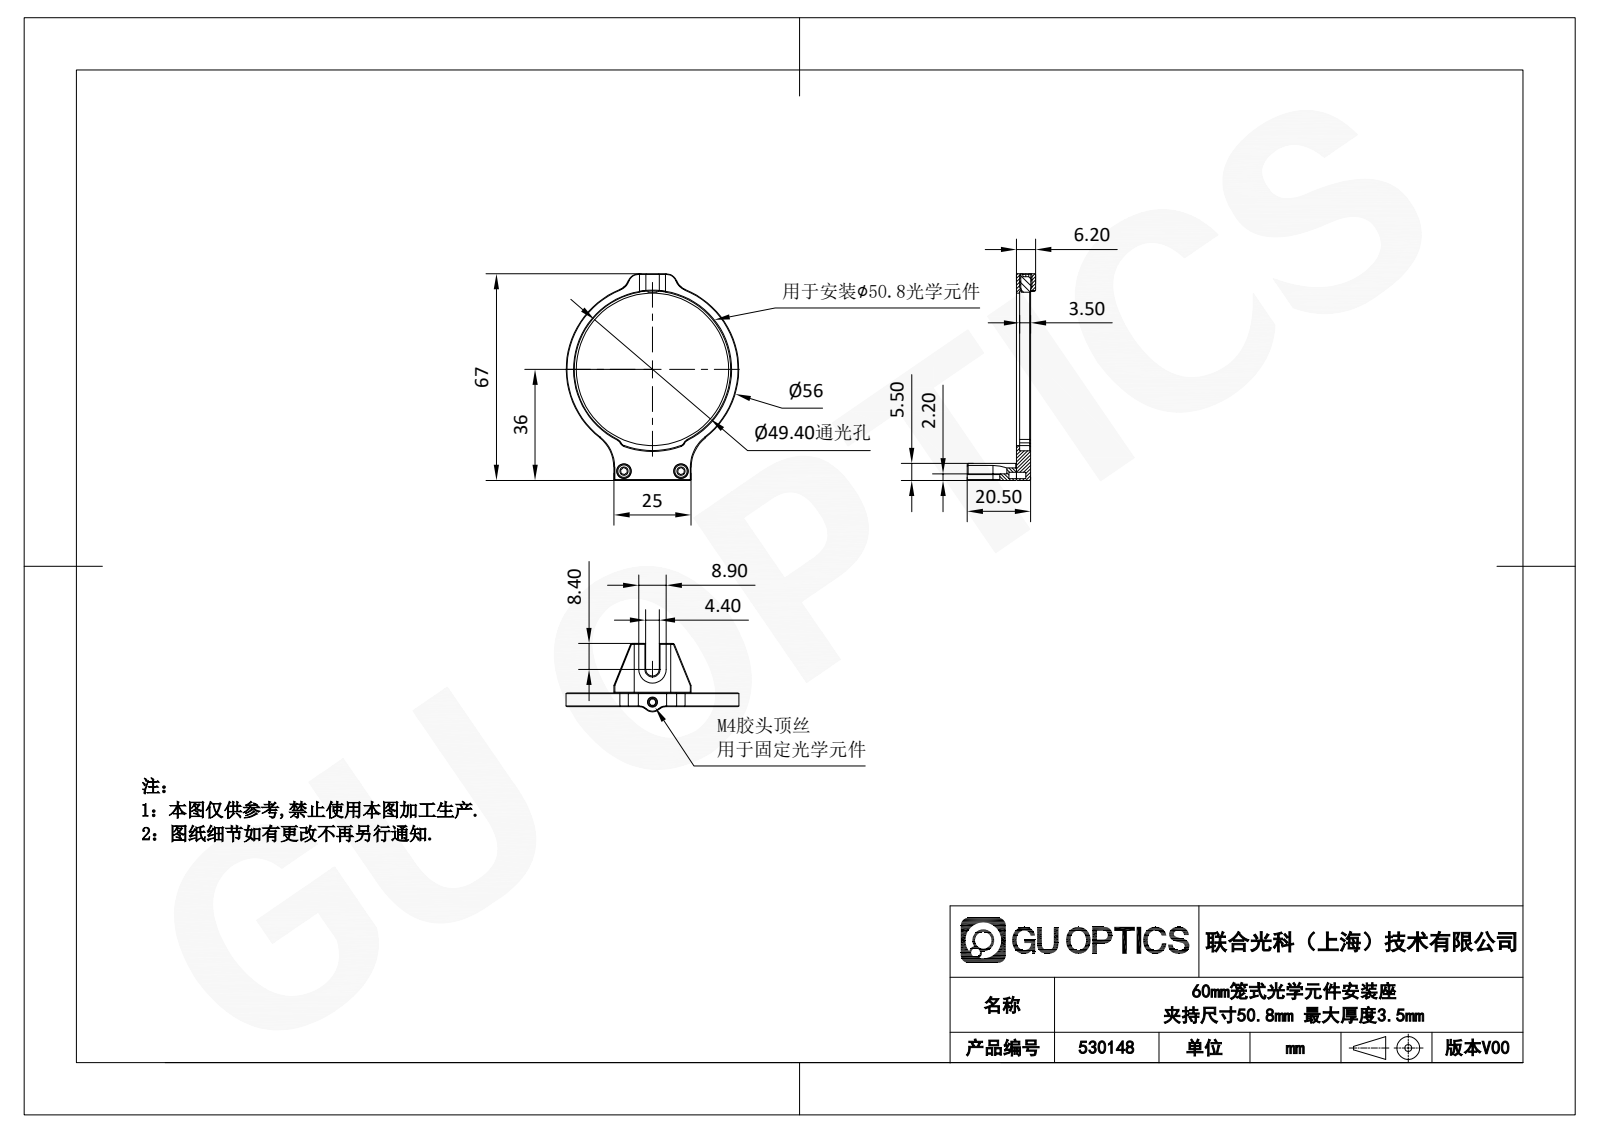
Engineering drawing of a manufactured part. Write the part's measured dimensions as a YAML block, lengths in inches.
part_name: "530148"
step_written_by: "SolidWorks 2020 (CONFIG_CONTROL_DESIGN)"
units: inches
bodies: {solids: 0, faces: 159, planar: 94, cylindrical: 25, other: 40}
overall_size: [2.638, 2.205, 0.873]
round_bosses_or_shafts:
  - {diameter: 0.189, count: 2}
  - {diameter: 2, count: 1}
  - {diameter: 1.945, count: 1}
  - {diameter: 0.13, count: 1}
  - {diameter: 0.118, count: 1}
partial_cylinders:
  - {radius: 0.079, count: 2}
  - {radius: 0.098, count: 2}
  - {radius: 0.118, count: 2}
  - {radius: 0.138, count: 2}
  - {radius: 0.197, count: 2}
  - {radius: 0.472, count: 2}
  - {radius: 0.087, count: 1}
  - {radius: 0.125, count: 1}
face_to_face_distances: [0.177, 0.039, 0.138, 0.217, 0.085, 0.131, 0.317, 0.667, 2.638, 2.553]
